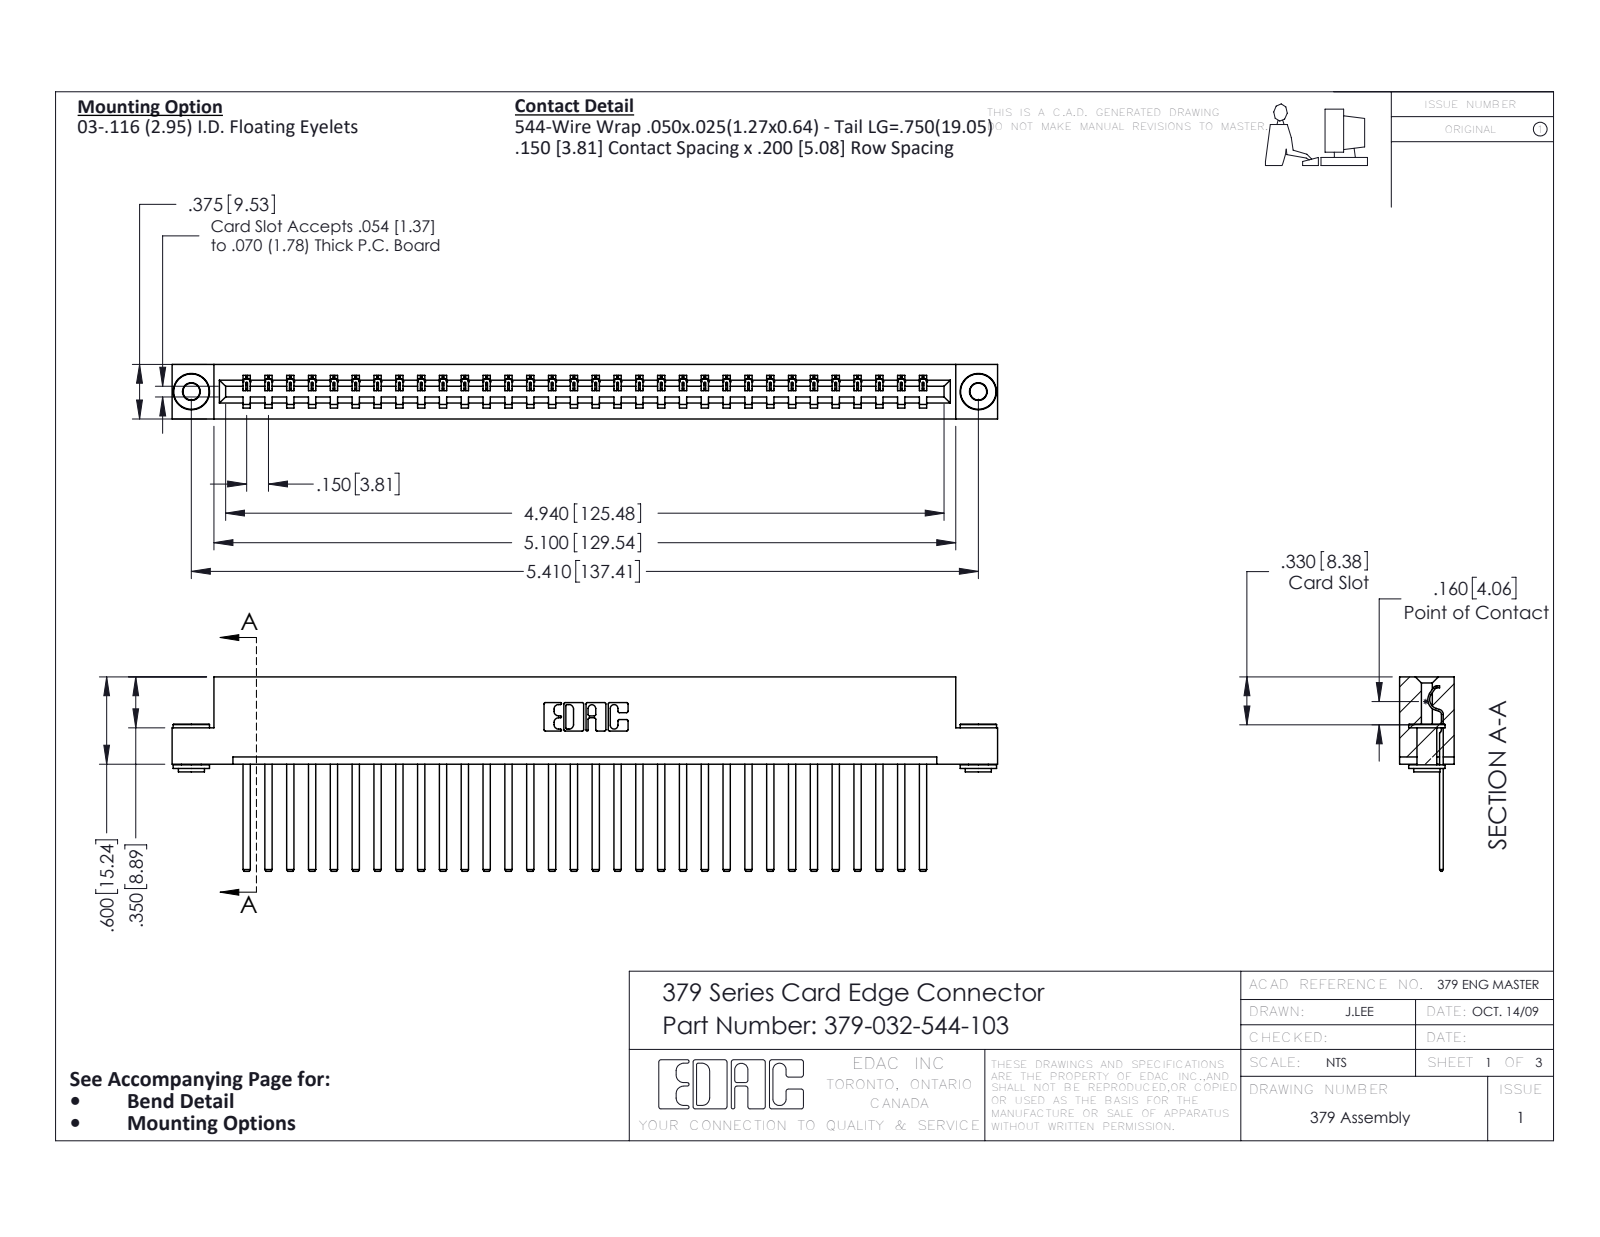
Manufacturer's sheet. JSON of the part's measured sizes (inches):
{"part_name": "379-032-544-103; 345-292-001_345-293-144; 345-250-002_345-250-002-102; 379 Part_Flush - .156 Dia - TH", "step_written_by": "SolidWorks 2016 (CONFIG_CONTROL_DESIGN)", "units": "inches", "bodies": {"solids": 35, "faces": 1816, "planar": 1296, "cylindrical": 512, "other": 8}, "overall_size": [5.675, 1.337, 0.375], "volume_in3": 0.941, "surface_area_in2": 26.63, "round_holes": [[0.116, 2], [0.156, 2]], "round_bosses_or_shafts": [[0.25, 2], [0.18, 2], [0.136, 2]], "partial_cylinders_radius": [[0.006, 64], [0.01, 22], [0.007, 6], [0.031, 6], [0.026, 3], [0.014, 1], [0.022, 1], [0.024, 1]], "face_to_face_distances": [0.3, 0.075, 0.375, 0.275, 0.025, 0.1, 0.225, 0.6, 0.2, 0.15], "hole_center_spacings": [5.41]}
